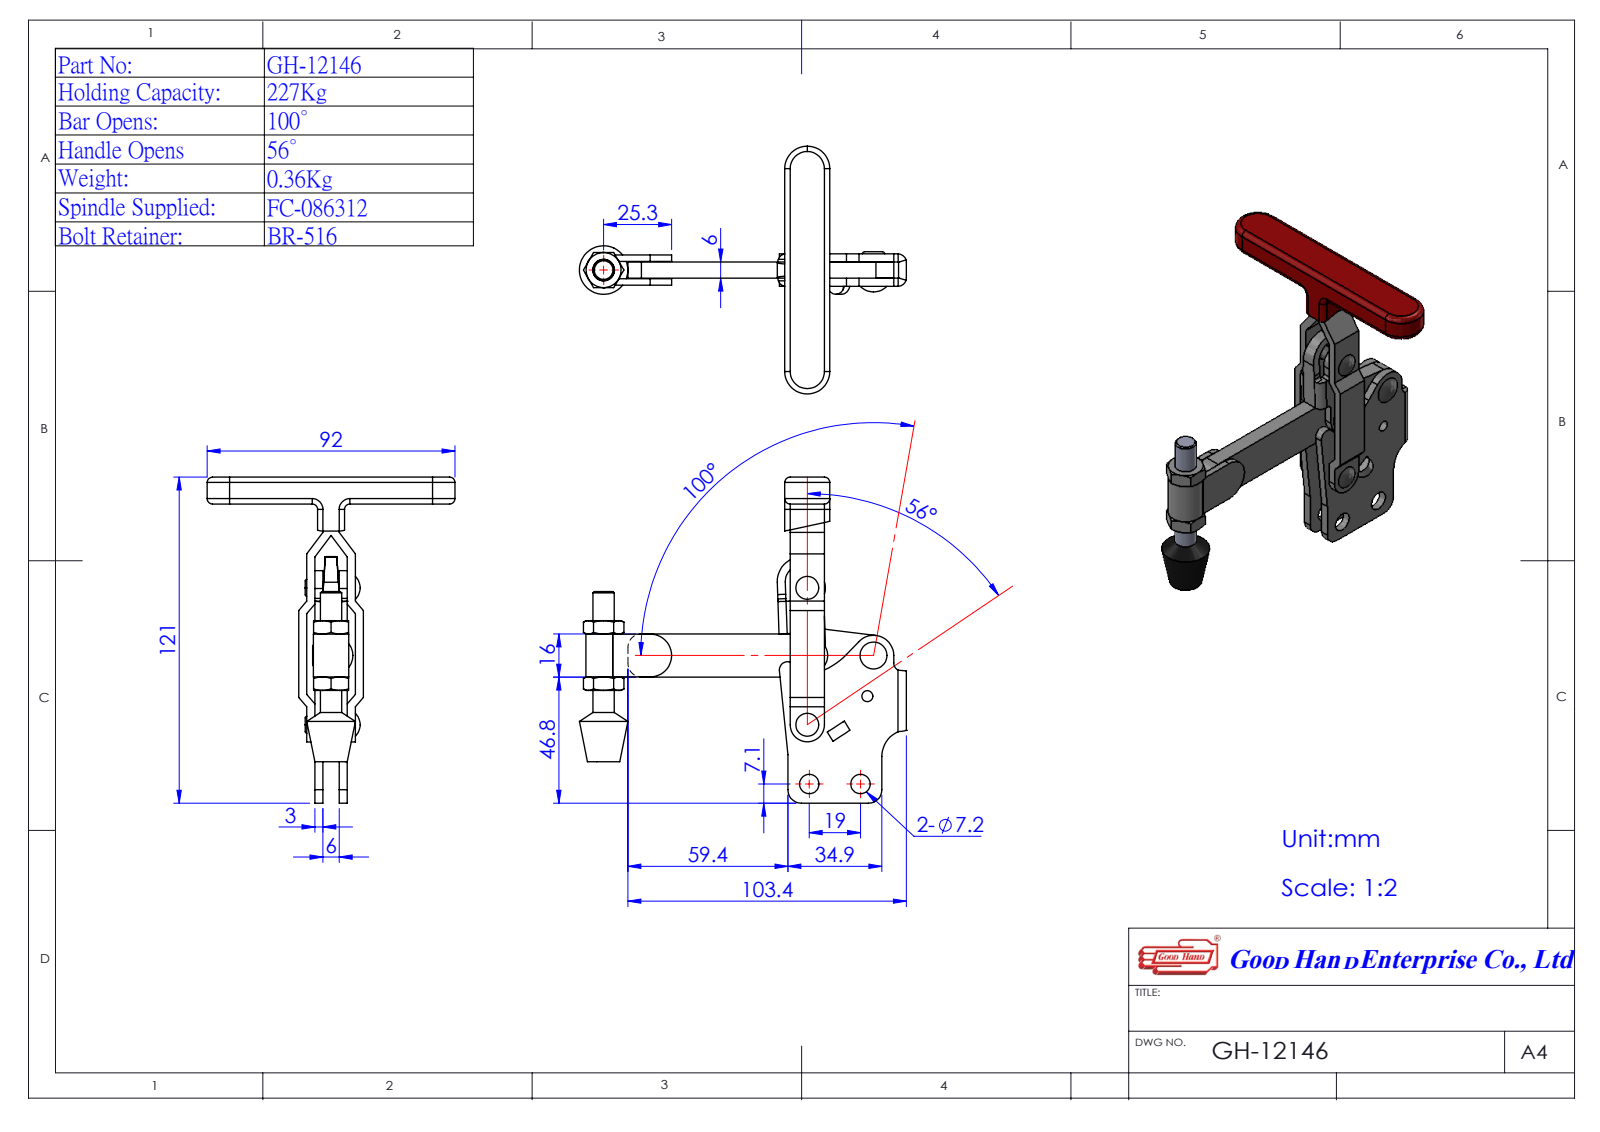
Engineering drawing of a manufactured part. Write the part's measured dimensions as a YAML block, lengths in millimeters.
part_name: "GH-12146(簡化); Group2^GH-12146(簡化); Group1^EMC12141; 11214008-1^GH-12146(簡化) (+2 more)"
step_written_by: "SolidWorks 2016 (AUTOMOTIVE_DESIGN)"
units: millimeters
bodies: {solids: 5, faces: 281, planar: 130, cylindrical: 99, other: 52}
overall_size: [121.41, 121, 92]
volume: 58129
surface_area: 33898
round_holes:
  - {diameter: 4, count: 5}
  - {diameter: 7.2, count: 2}
round_bosses_or_shafts:
  - {diameter: 7.93, count: 1}
partial_cylinders:
  - {radius: 7.5, count: 4}
  - {radius: 0.1, count: 2}
  - {radius: 1, count: 2}
  - {radius: 2, count: 2}
  - {radius: 2.42, count: 2}
  - {radius: 3, count: 2}
  - {radius: 3.1, count: 2}
  - {radius: 5, count: 2}
face_to_face_distances: [3, 9, 6, 12, 15, 10, 18, 8.8, 2, 6.4]
hole_center_spacings: [15.27, 19, 22.01, 23.4, 24.69, 25.13, 25.73, 25.95]
